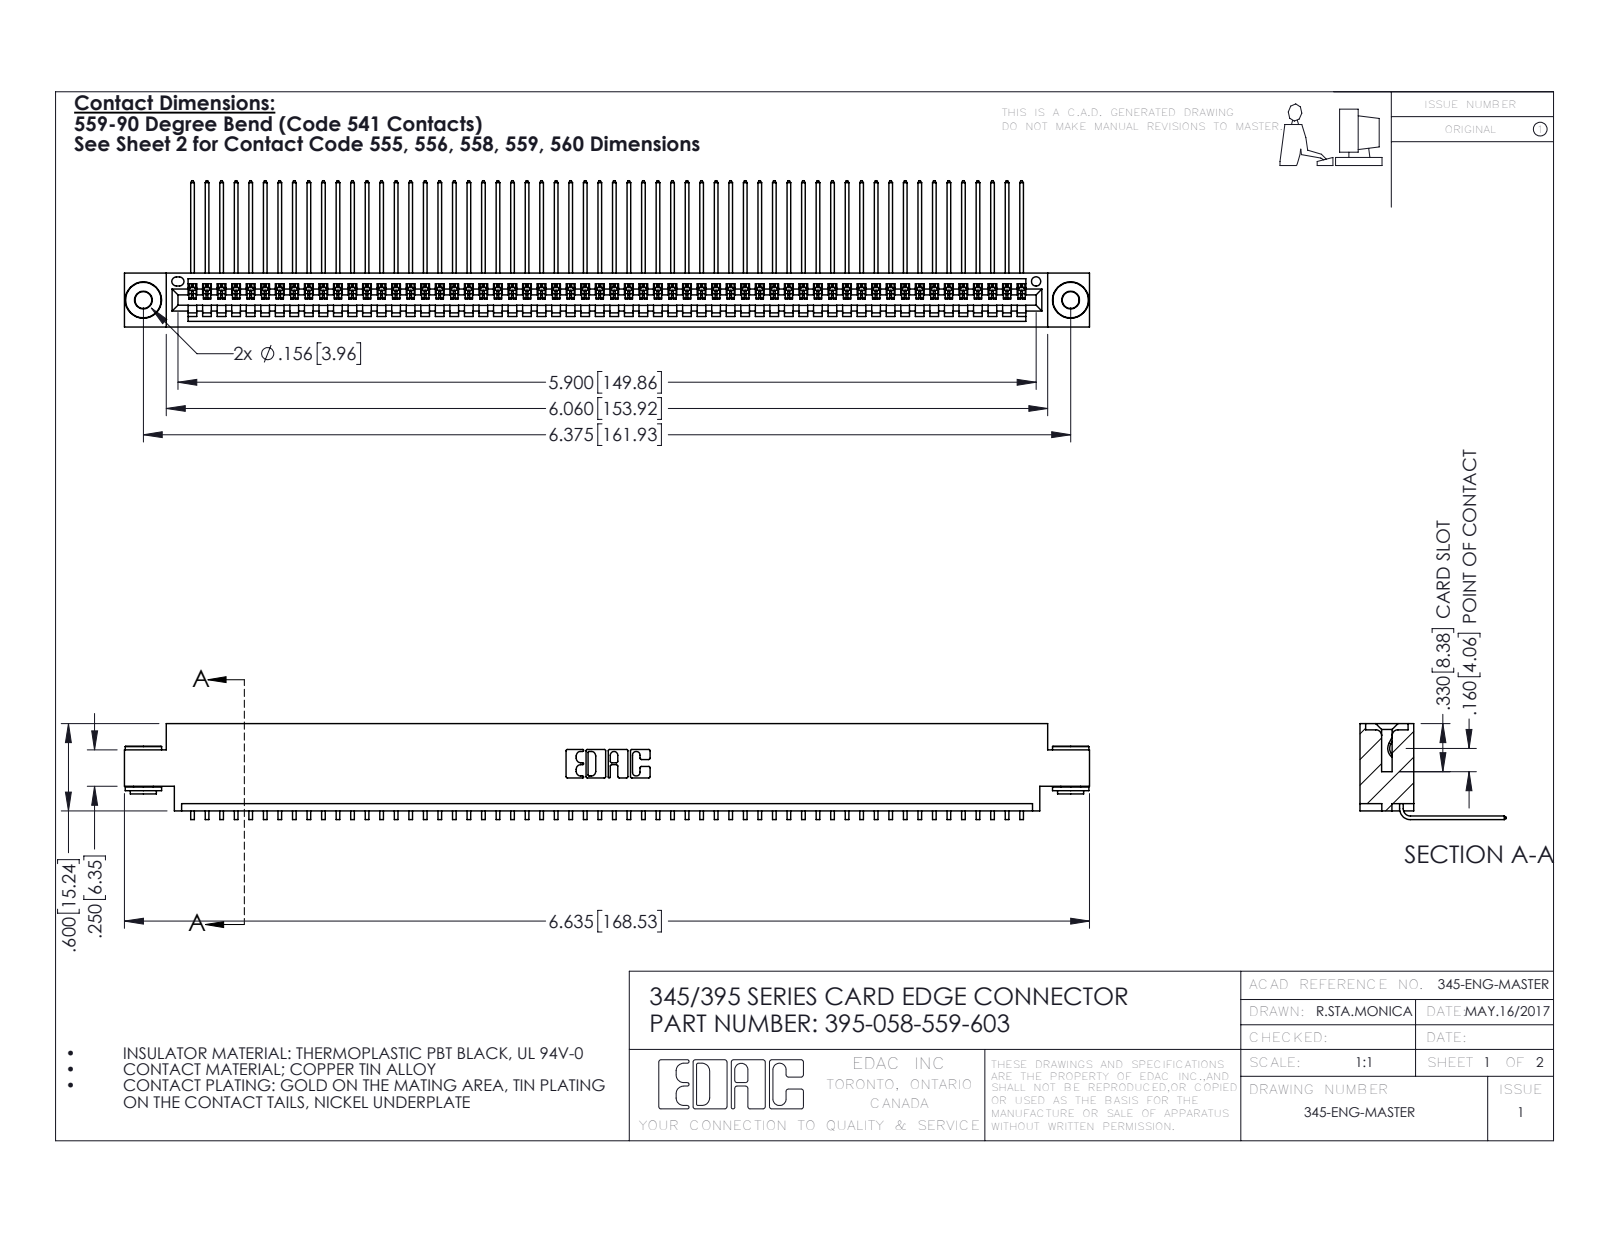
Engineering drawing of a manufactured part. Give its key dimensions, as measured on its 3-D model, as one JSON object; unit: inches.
{"part_name": "345-292-001_558 559 Tail - 1; 345 Part_0.170 Offset - 0.156 Dia-TH; 345-250-002_345-250-002-102; 395-058-559-603", "step_written_by": "SolidWorks 2016 (CONFIG_CONTROL_DESIGN)", "units": "inches", "bodies": {"solids": 61, "faces": 3648, "planar": 2530, "cylindrical": 1110, "other": 8}, "overall_size": [6.635, 1.005, 0.659], "volume_in3": 0.991, "surface_area_in2": 36.07, "round_holes": [[0.116, 2], [0.156, 2], [0.064, 1]], "round_bosses_or_shafts": [[0.25, 2], [0.18, 2], [0.136, 2]], "partial_cylinders_radius": [[0.006, 116], [0.01, 22], [0.007, 6], [0.031, 6], [0.026, 3], [0.031, 2], [0.04, 2], [0.014, 1]], "face_to_face_distances": [0.072, 0.298, 0.37, 0.2, 0.098, 0.272, 0.025, 0.225, 0.175, 0.149], "hole_center_spacings": [0.27, 6.139, 6.375]}
